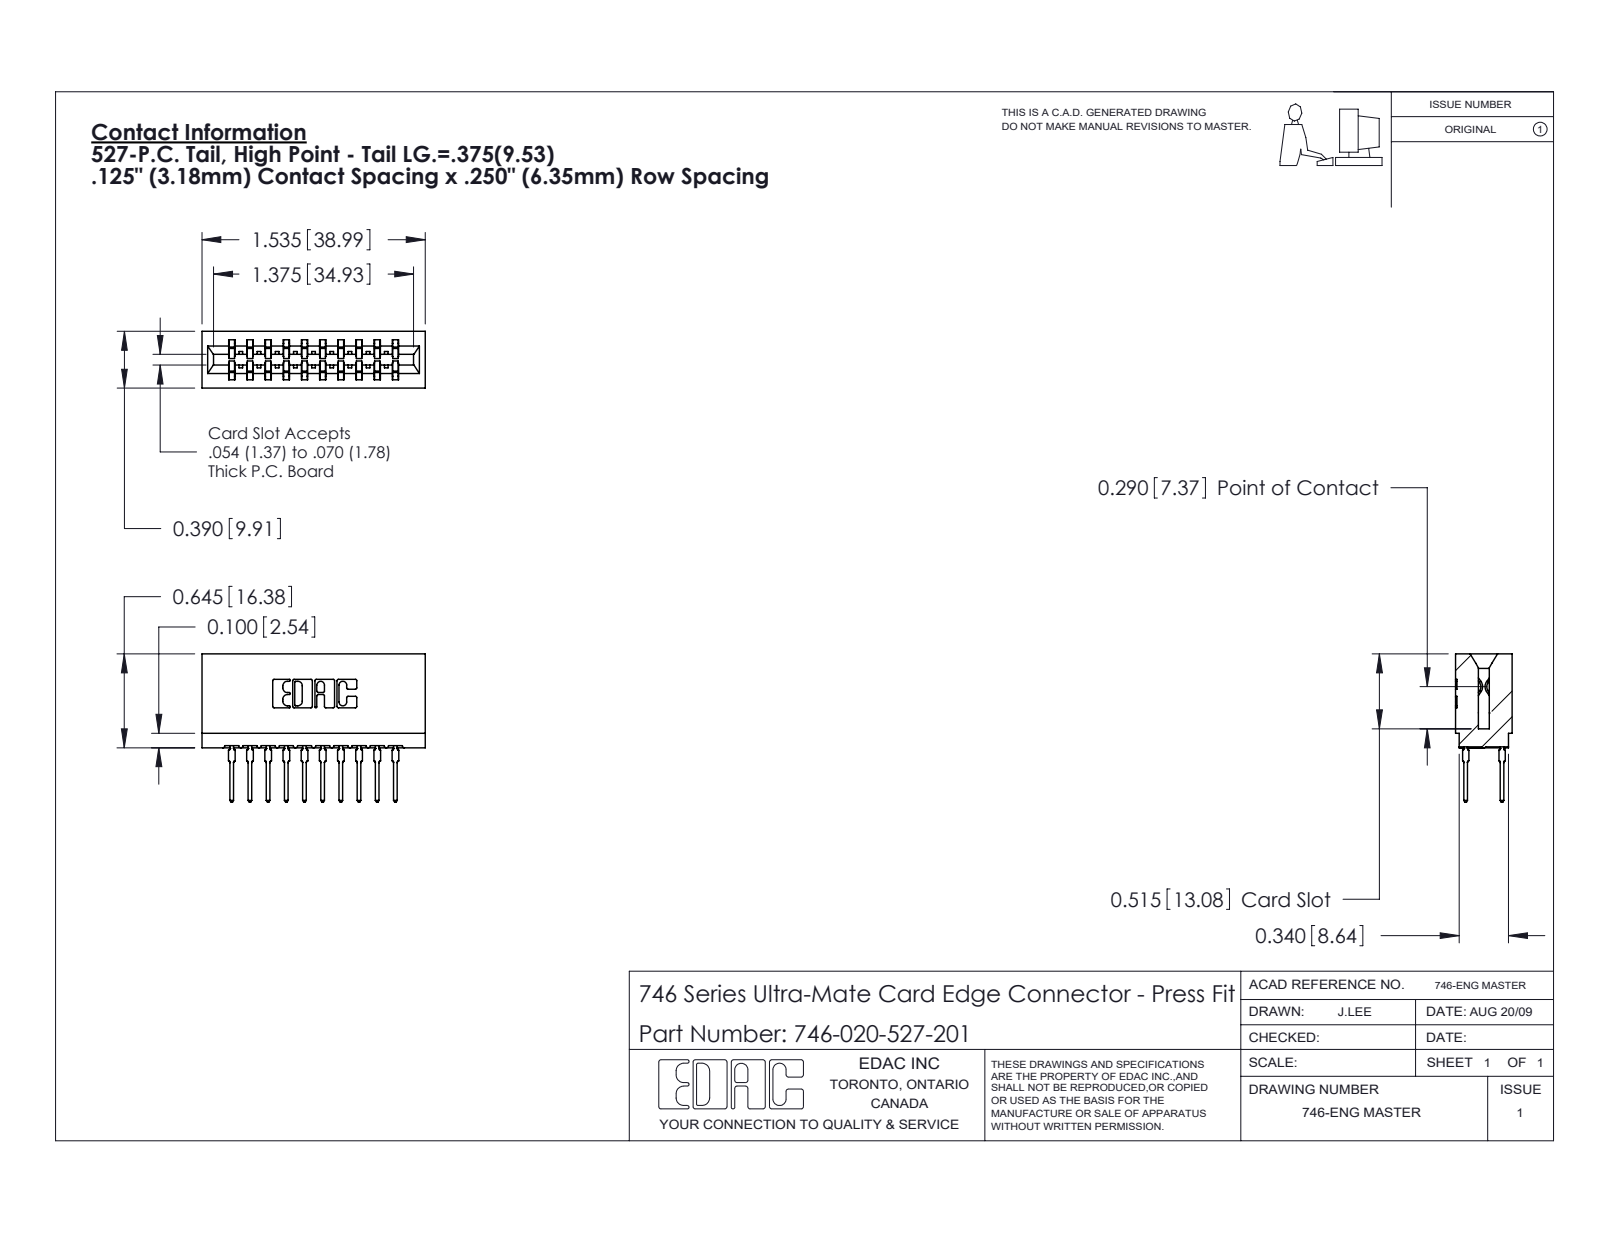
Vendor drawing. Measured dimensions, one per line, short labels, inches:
name: 746-292-001_527; 746 Part_.515 Slot Depth - 01; 746-020-527-201
written by: SolidWorks 2020 (CONFIG_CONTROL_DESIGN)
unit: in
bodies: 21 solids, 1887 faces (975 planar, 392 cylindrical, 520 other)
size: 1.535 × 1.019 × 0.39
volume: 0.27 in³; area: 10.24 in²
rounds: 40× R0.021, 22× R0.01, 11× R0.015, 8× R0.005, 8× R0.011, 6× R0.007, 6× R0.031, 3× R0.026
face distances: 0.25, 0.333, 0.057, 0.5, 0.125, 0.042, 0.375, 0.208, 0.125, 0.39
